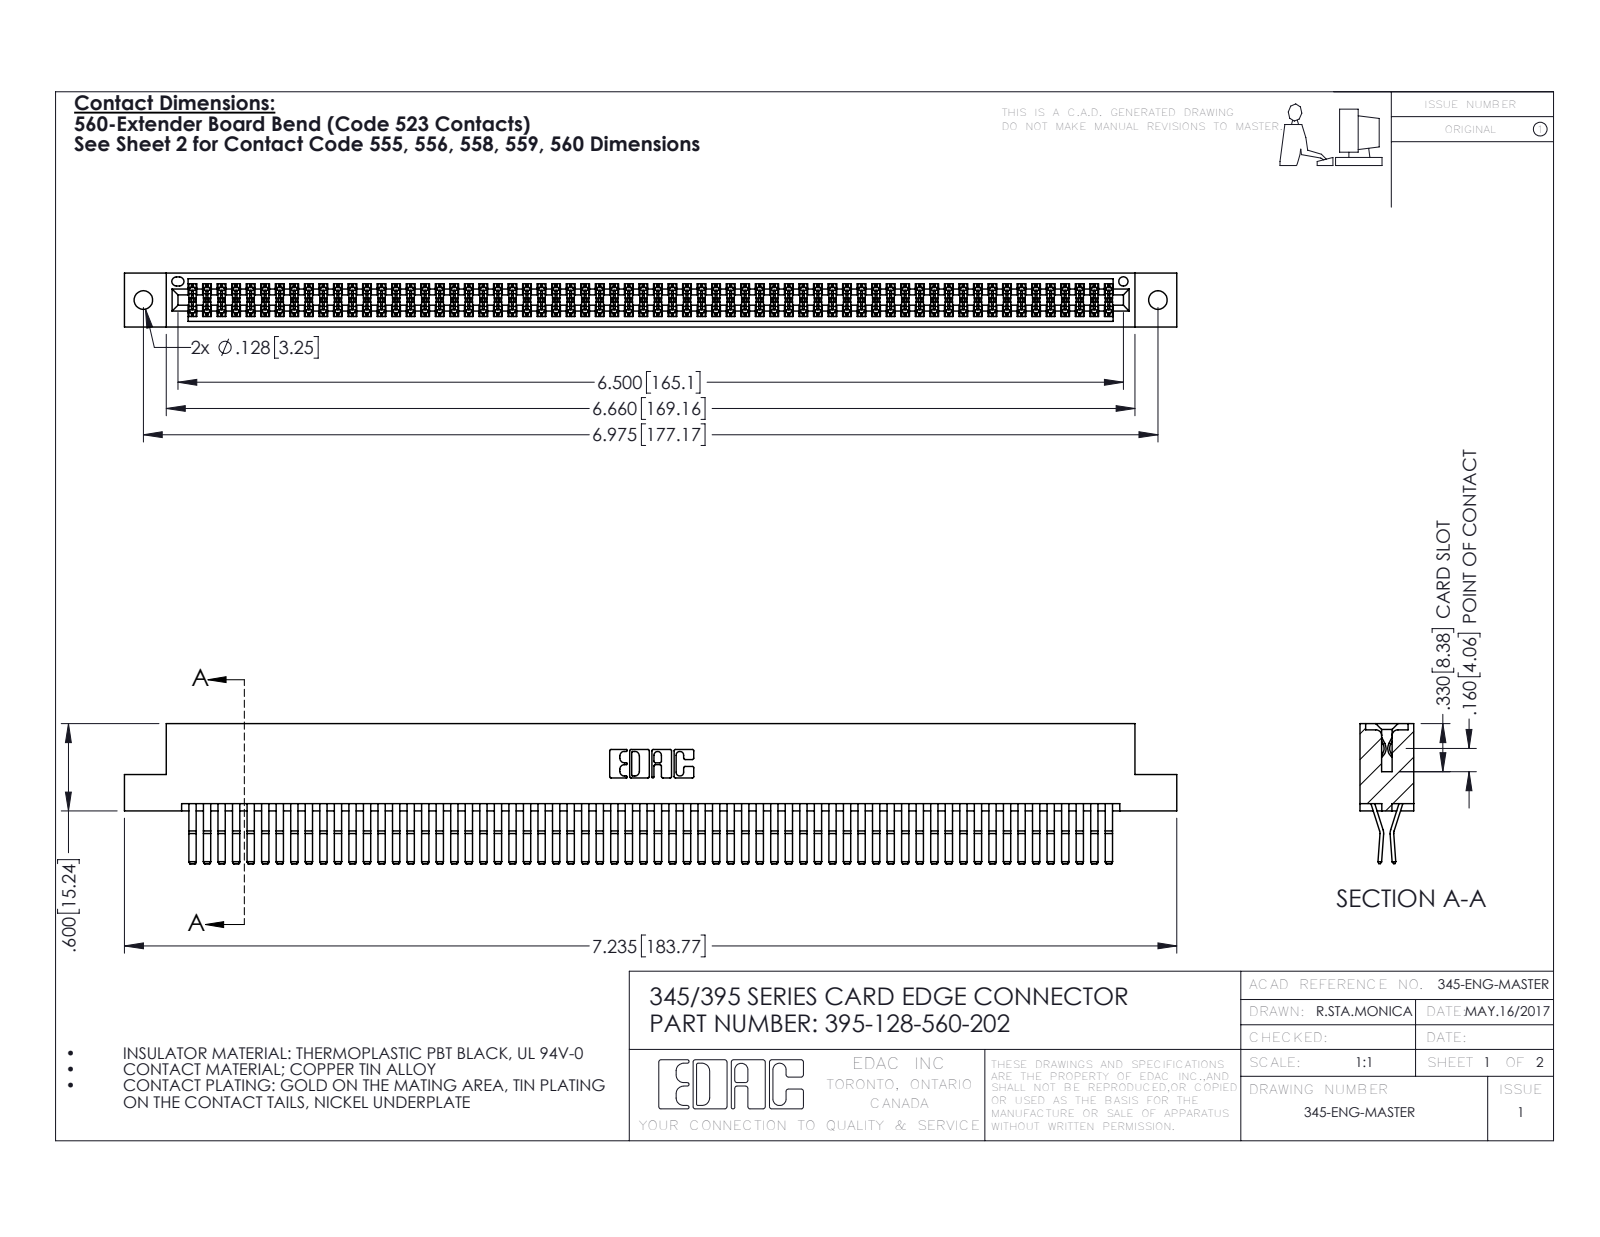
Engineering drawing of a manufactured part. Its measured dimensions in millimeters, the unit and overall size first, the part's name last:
Units: millimetres
Overall size (bounding box): 183.8 × 24.4 × 9.4
Round holes (diameter × count): ⌀3.3 ×2, ⌀1.6 ×1
Partial cylindrical surfaces — rounded edges, fillets, slot ends (radius × count): R0.2 ×192, R0.3 ×22, R0.2 ×6, R0.8 ×6, R0.7 ×3, R0.3 ×2, R0.4 ×2, R0.5 ×2
Main face-to-face distances: 0.6, 7.6, 1.8, 9.4, 5.1, 2.5, 6.9, 5.7, 4.4, 3.8
Hole centre spacings: 6.9, 171.2, 177.2
Volume: 18 860 mm³ · Surface area: 30 190 mm²
Bodies: 129 solids, 6782 faces (4304 planar, 2478 cylindrical, 0 other)
Part name (STEP PRODUCT): 395-128-560-202; 345-292-001_560 Tail; 345 Part_Flush Mounting Lugs - 0.128 Dia
STEP written by: SolidWorks 2016 (CONFIG_CONTROL_DESIGN)
